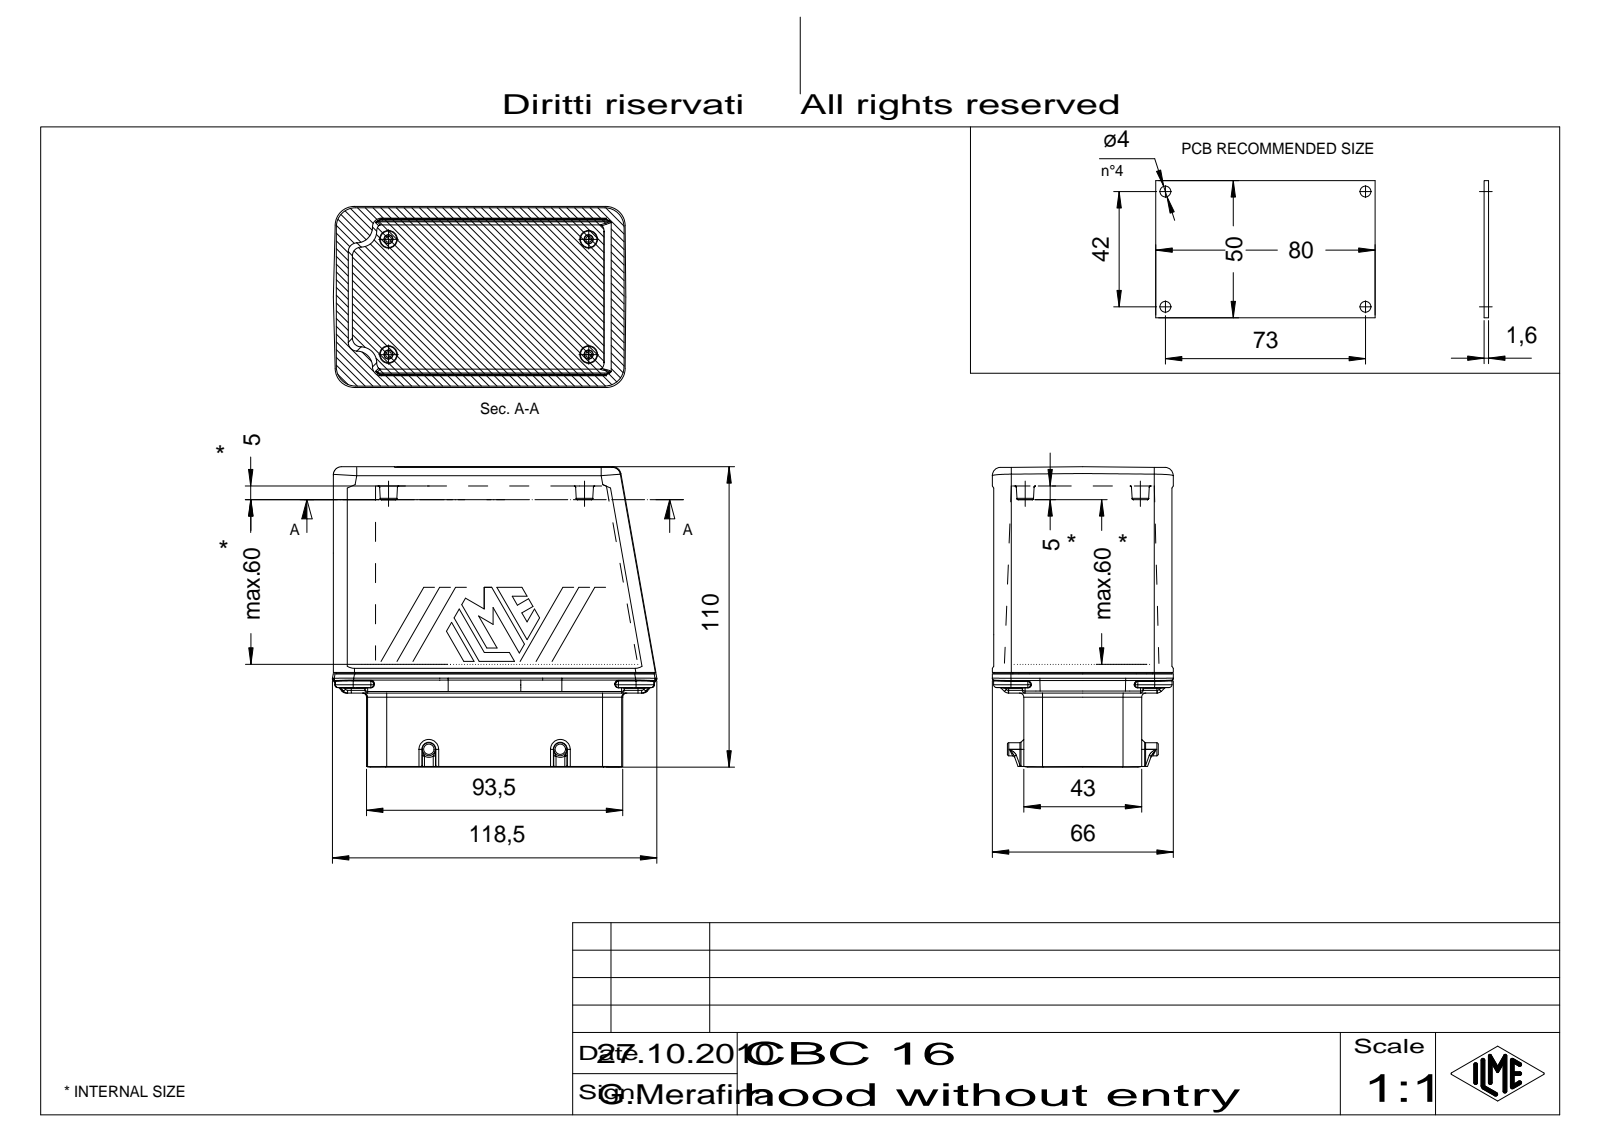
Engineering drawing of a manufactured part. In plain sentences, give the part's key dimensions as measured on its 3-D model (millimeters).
The part is named "53848_Body_1". Its 3-D file was written by "CoCreate Modeling 16.00A 16-Aug-2008 (C) Parametric Technology GmbH (AUTOMOTIVE_DESIGN)". It is 1 solid with 644 faces: 332 planar, 148 cylindrical and 164 other. Overall it measures 117.26 by 108.97 by 66.01 millimeters. Its volume is 611 416 cubic millimeters and its surface area 56 912 square millimeters. Round bosses or shafts: 2 of diameter 4.8. Partial cylindrical surfaces (rounded edges, fillets, slot ends): 44 of radius 1, 18 of radius 0.3, 12 of radius 7, 10 of radius 3, 8 of radius 0.5, 6 of radius 1.5, 4 of radius 4.2, 4 of radius 5. The main face-to-face distances are 65.01, 82.21, 0.4, 65.41, 11, 54.01, 54, 43, 11.01, 11.4.
